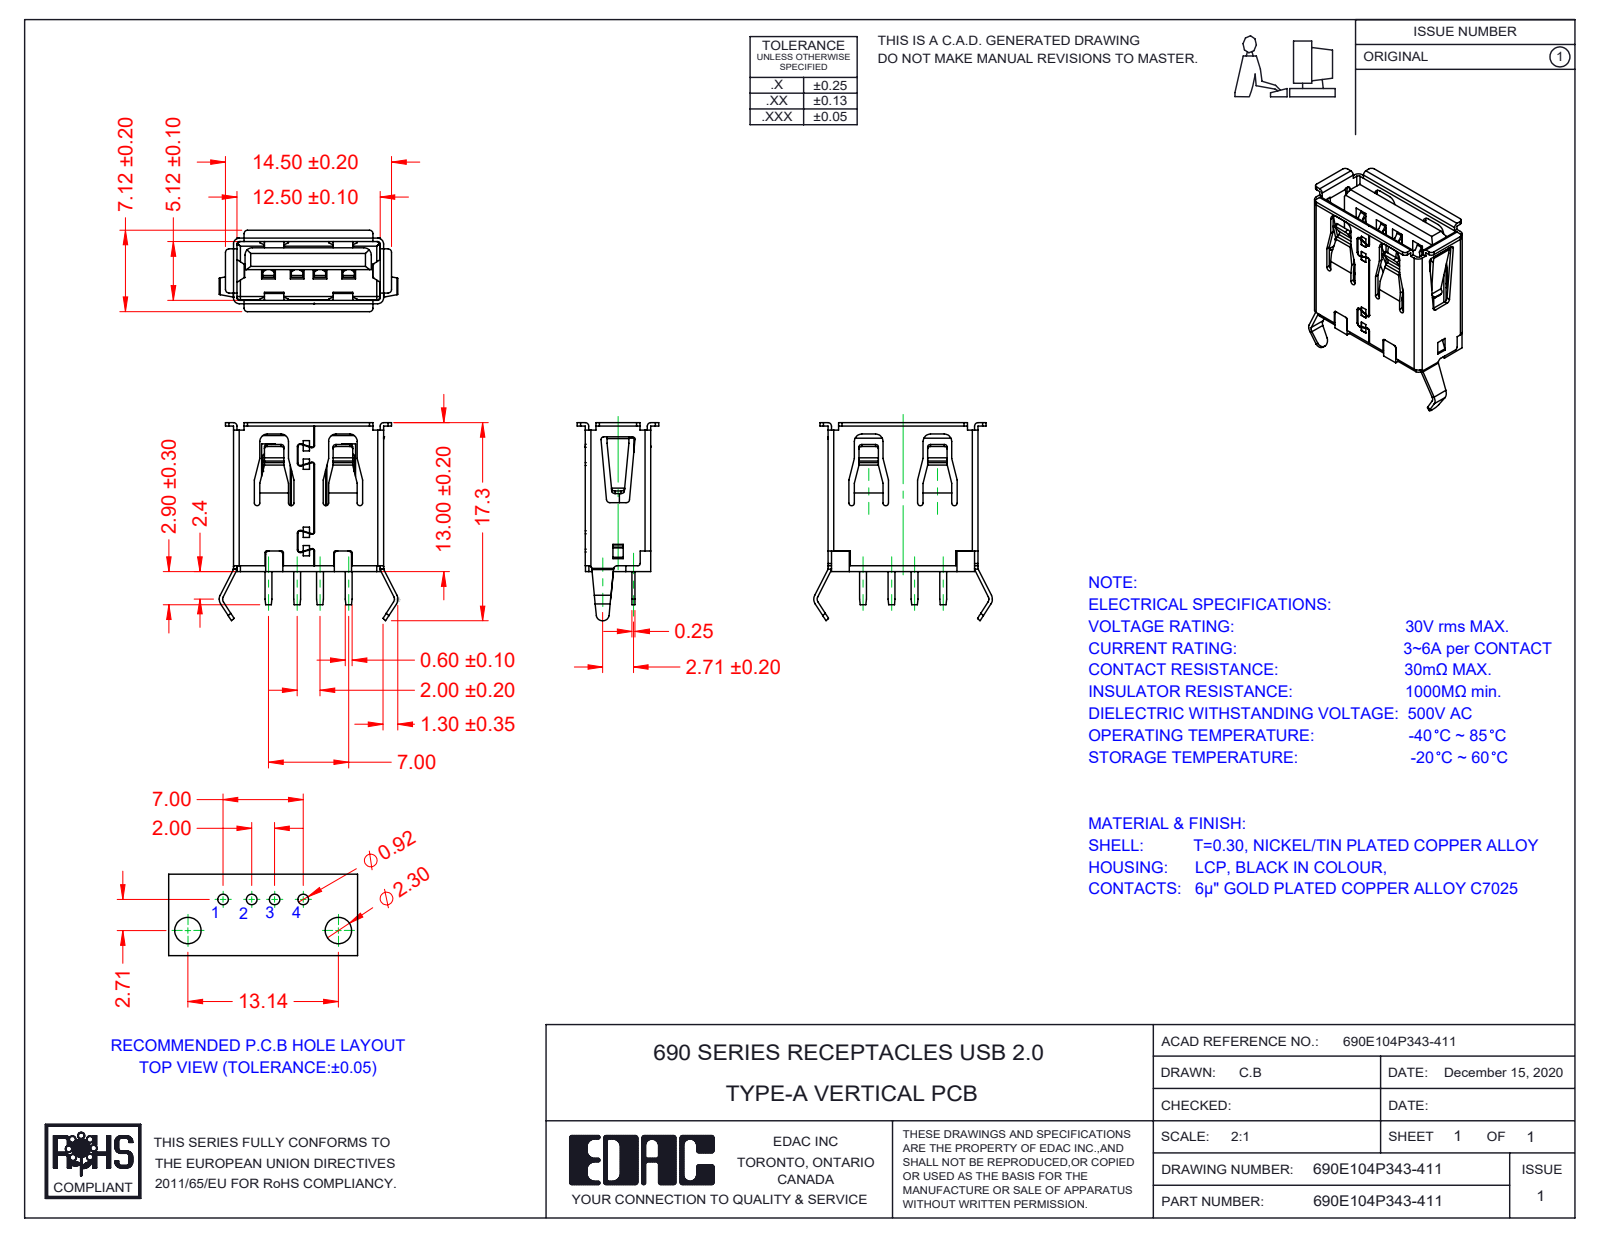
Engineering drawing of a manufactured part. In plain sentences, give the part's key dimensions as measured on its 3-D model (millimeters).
The part is named "Contacts 690E104-X43-4XX; Shell 690E104-X43-4XX; Insulator 690E104-X43-4XX_Black; 690E104P343-411". Its 3-D file was written by "SolidWorks 2020 (AUTOMOTIVE_DESIGN)". It is 6 solids with 690 faces: 491 planar, 194 cylindrical and 5 other. Overall it measures 17.3 by 15.6 by 7.12 millimeters. Its volume is 462 cubic millimeters and its surface area 1 764 square millimeters. Partial cylindrical surfaces (rounded edges, fillets, slot ends): 37 of radius 0.2, 33 of radius 0.3, 17 of radius 0.15, 14 of radius 0.25, 10 of radius 0.5, 4 of radius 0.24, 4 of radius 0.56, 4 of radius 0.65. The main face-to-face distances are 5.42, 5.72, 5.12, 1.39, 1.09, 4.03, 4.33, 12.8, 0.55, 4.5.
